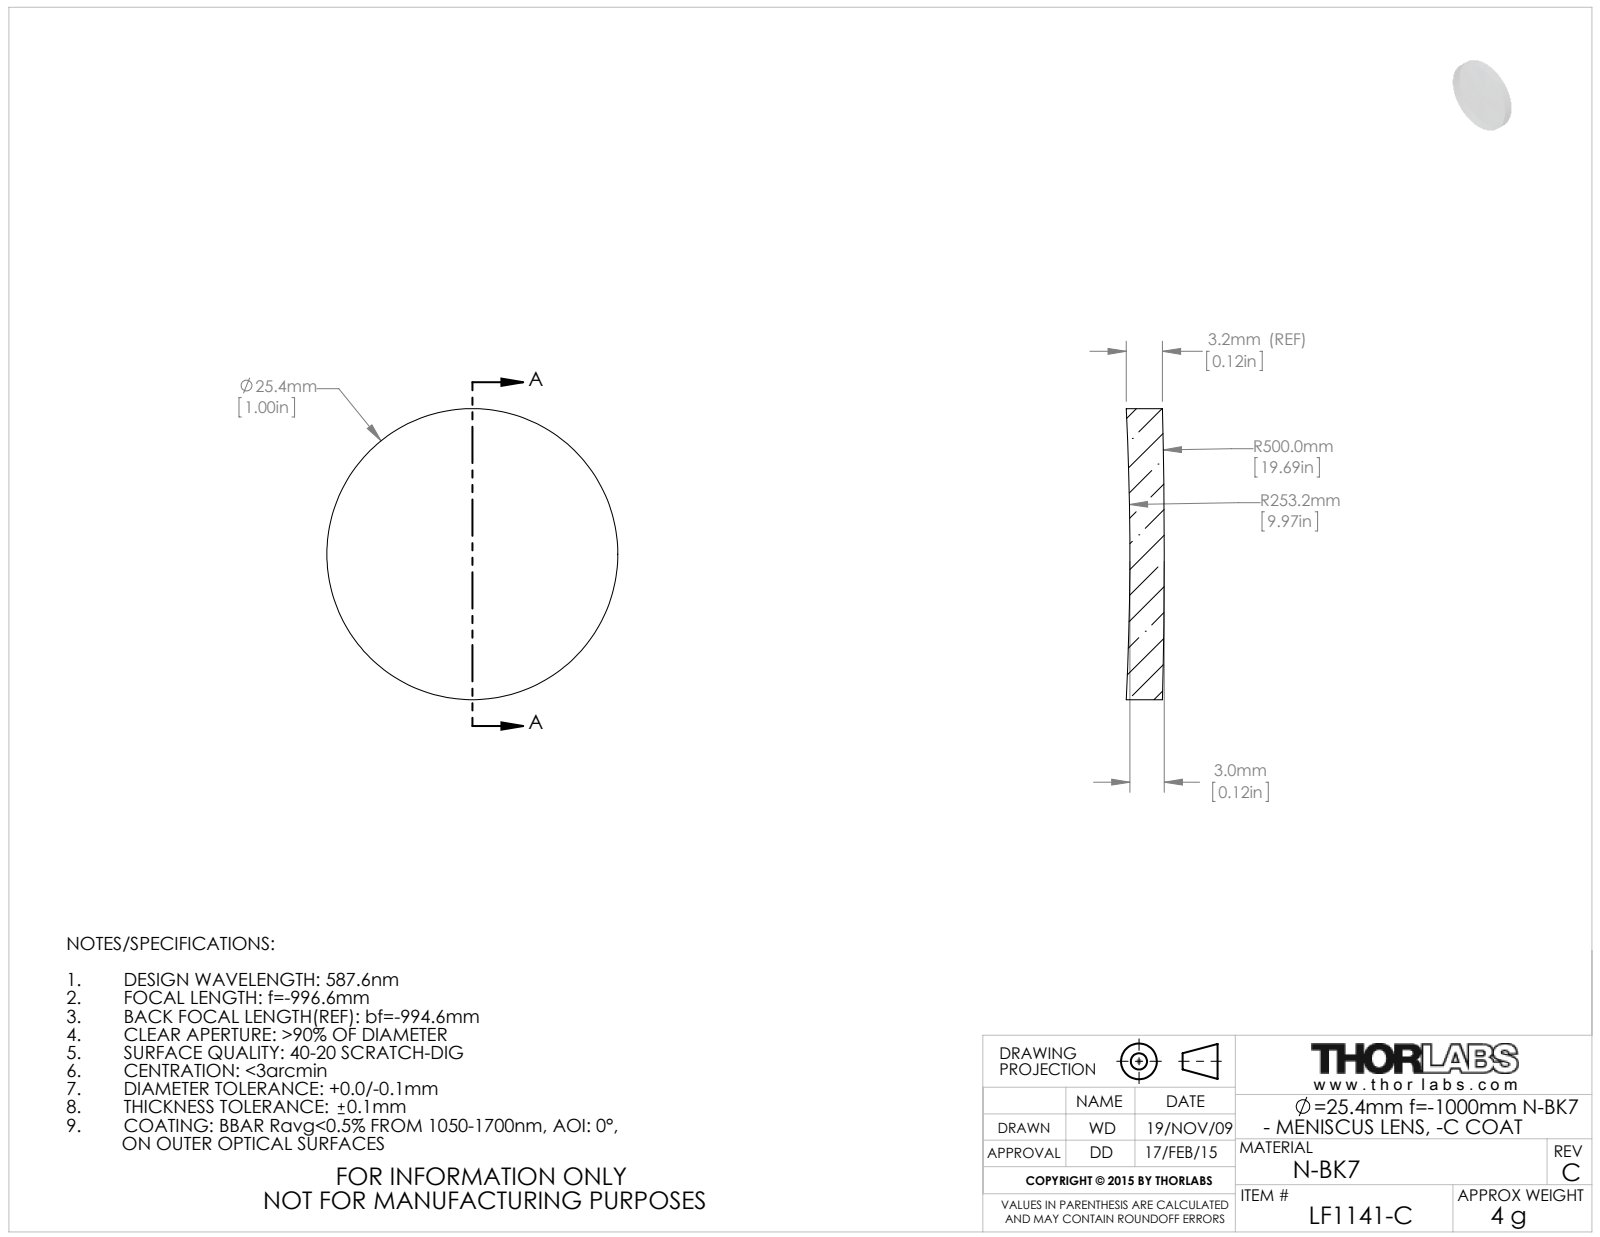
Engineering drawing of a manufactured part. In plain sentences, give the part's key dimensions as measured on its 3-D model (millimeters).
The part is named "4913-E0W". Its 3-D file was written by "SolidWorks 2009 (AUTOMOTIVE_DESIGN)". It is 1 solid with 6 faces: 0 planar, 2 cylindrical and 4 other. Overall it measures 25.4 by 25.4 by 3.32 millimeters. Its volume is 1 560 cubic millimeters and its surface area 1 266 square millimeters. Round bosses or shafts: 1 of diameter 25.4.
